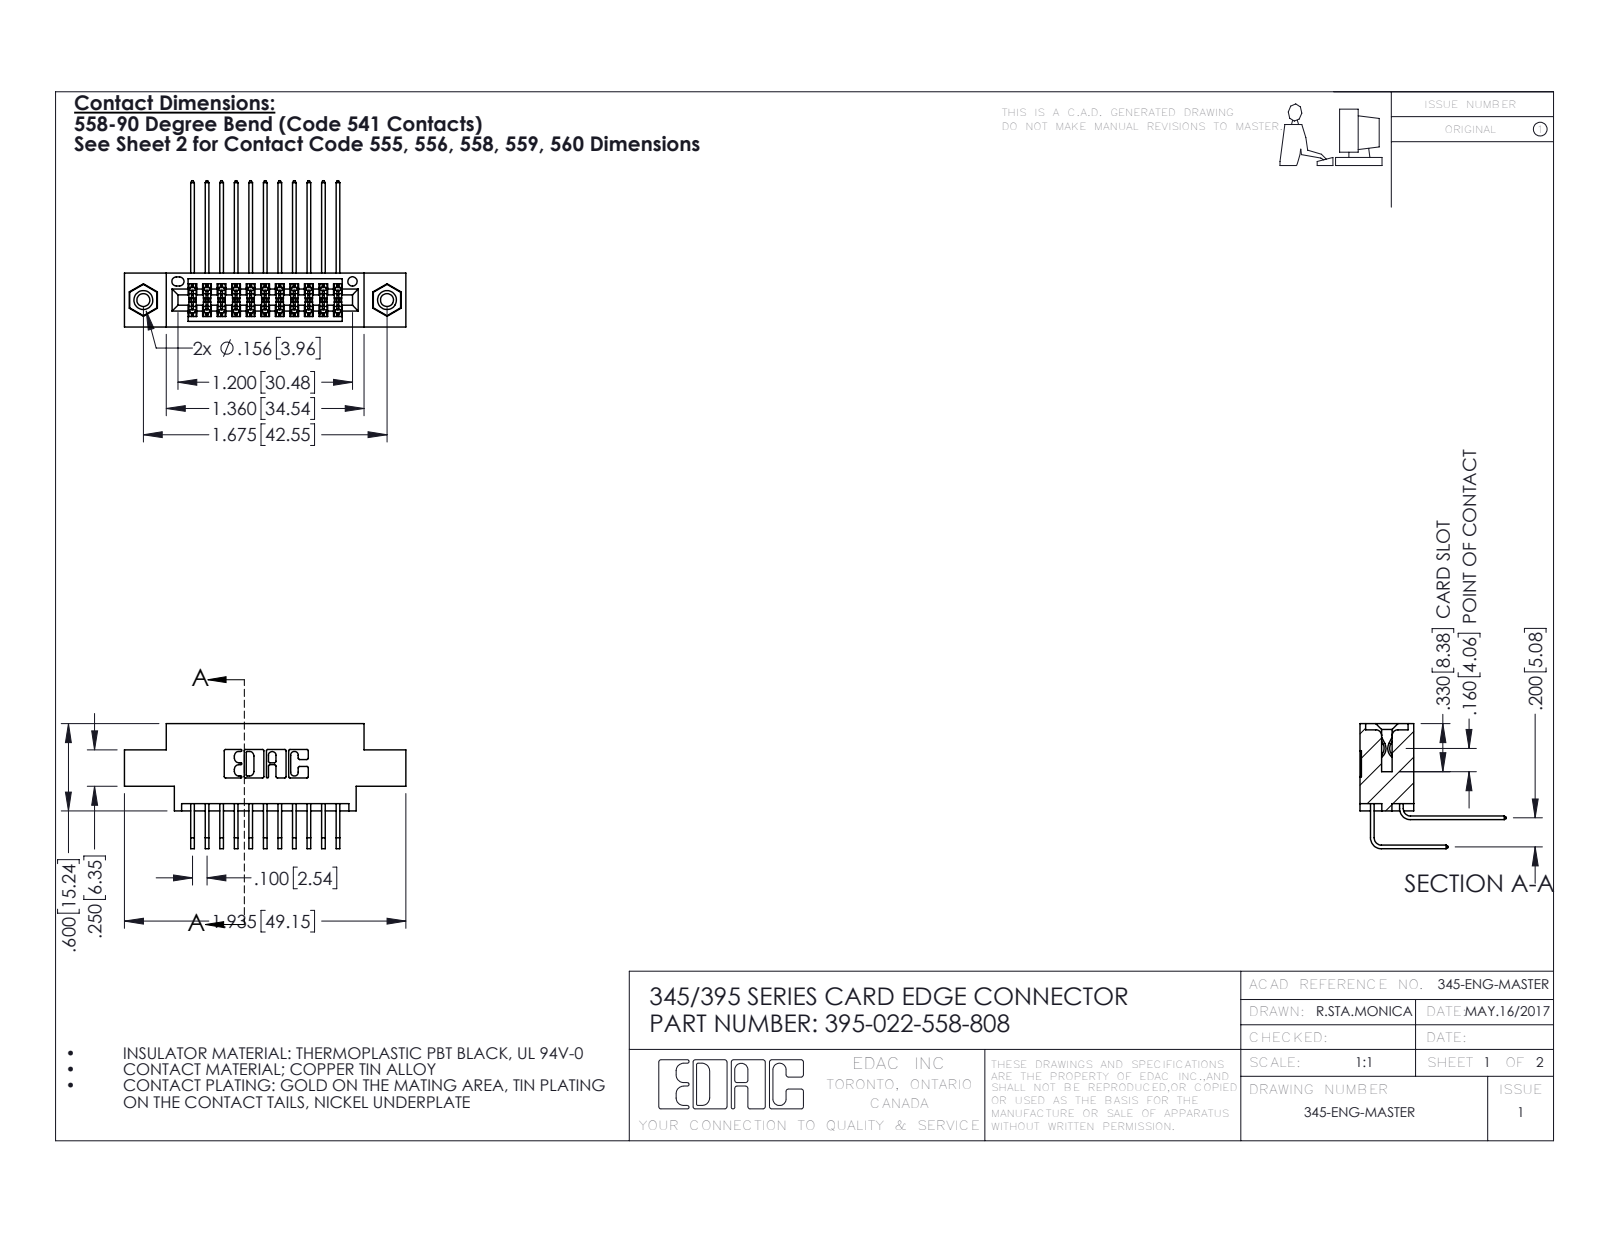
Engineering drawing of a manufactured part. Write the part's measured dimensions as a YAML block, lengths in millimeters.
part_name: "345-292-001_558 Tail - 2; 345 Part_0.170 Offset - 0.156 Dia-TI; 395-022-558-808; 345-292-001_558 559 Tail - 1 (+1 more)"
step_written_by: "SolidWorks 2016 (CONFIG_CONTROL_DESIGN)"
units: millimeters
bodies: {solids: 25, faces: 1334, planar: 886, cylindrical: 432, other: 16}
overall_size: [49.1, 25.5, 21.8]
volume: 4490
surface_area: 6794
round_holes:
  - {diameter: 2.3, count: 2}
  - {diameter: 3.2, count: 2}
  - {diameter: 4, count: 2}
  - {diameter: 1.6, count: 1}
round_bosses_or_shafts:
  - {diameter: 3.9, count: 2}
partial_cylinders:
  - {radius: 0.2, count: 34}
  - {radius: 0.3, count: 22}
  - {radius: 0.2, count: 6}
  - {radius: 0.8, count: 6}
  - {radius: 0.7, count: 3}
  - {radius: 0.4, count: 2}
  - {radius: 0.5, count: 2}
  - {radius: 0.6, count: 2}
face_to_face_distances: [5.1, 1.8, 7.6, 9.4, 2.5, 6.9, 0.6, 2.5, 5.7, 4.4]
hole_center_spacings: [6.9, 36.7, 42.5]
